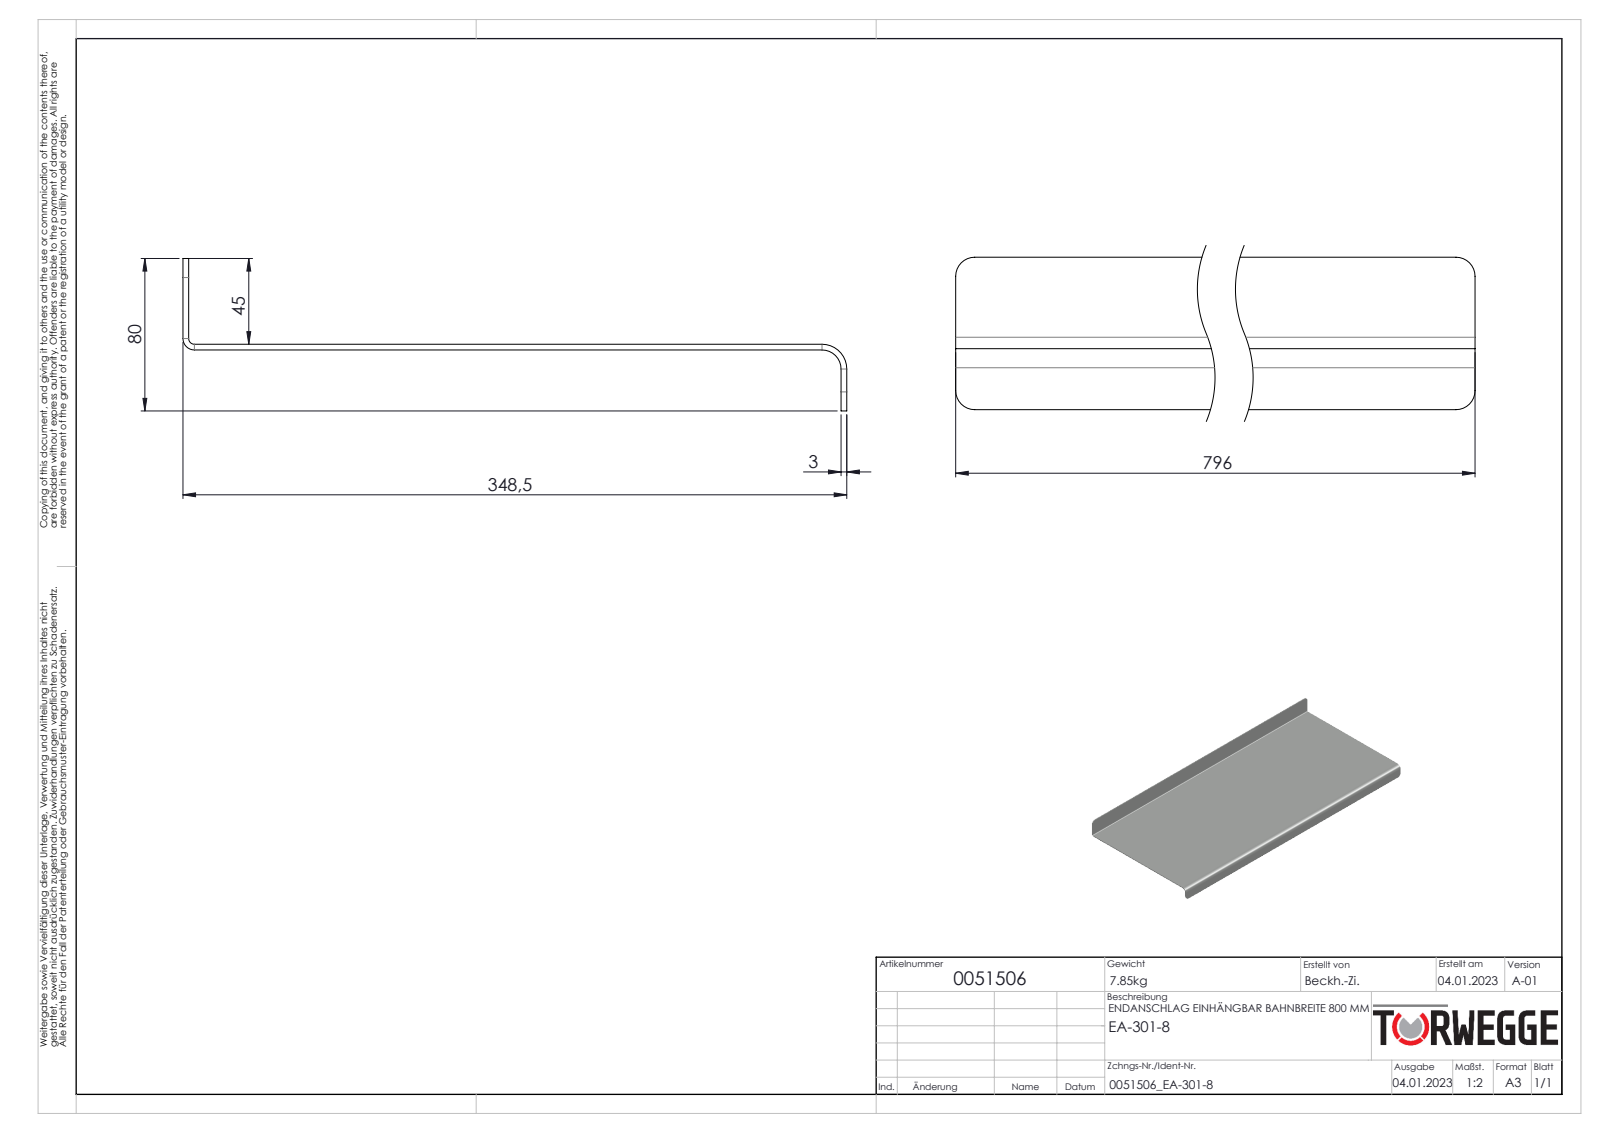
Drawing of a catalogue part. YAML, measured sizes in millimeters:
part_name: "0051506"
step_written_by: "SolidWorks 2020 (AUTOMOTIVE_DESIGN)"
units: millimeters
bodies: {solids: 1, faces: 26, planar: 18, cylindrical: 8, other: 0}
overall_size: [796, 348.5, 80]
volume: 999437
surface_area: 673528
partial_cylinders:
  - {radius: 10, count: 5}
  - {radius: 3, count: 1}
  - {radius: 6, count: 1}
  - {radius: 13, count: 1}
face_to_face_distances: [3, 345.5, 342.5, 348.5, 32, 35, 80, 48, 45, 796]
